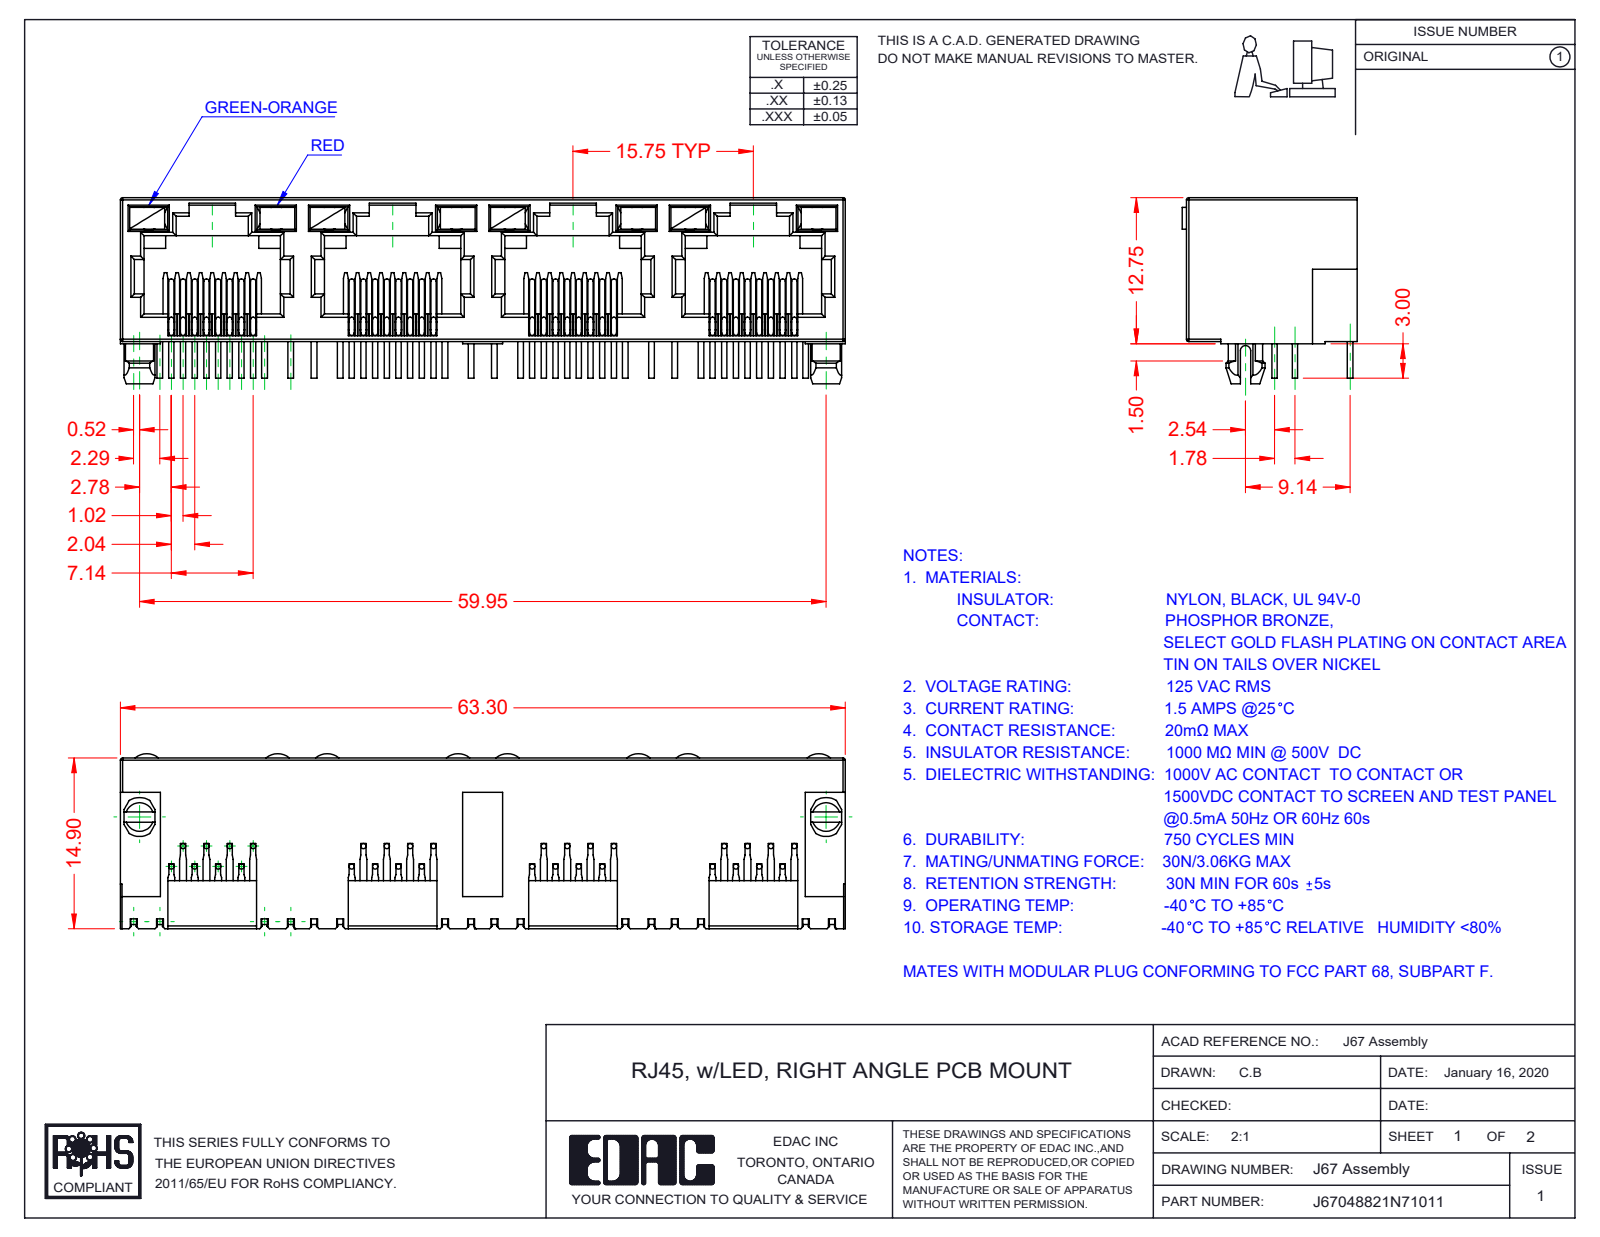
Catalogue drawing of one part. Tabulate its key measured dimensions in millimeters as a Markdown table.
| quantity | value |
| --- | --- |
| part name | J67048822N72011; 67 LED LH_7-Green-Orange; 67 LED RH_2-Red; 67 Contacts (+1 more) |
| STEP written by | SolidWorks 2016 (CONFIG_CONTROL_DESIGN) |
| units | millimeters |
| bodies | 41 solids, 2473 faces (1781 planar, 484 cylindrical, 208 other) |
| overall size | 63.3 × 16.25 × 15.28 |
| volume | 5 159 mm³ |
| surface area | 11 573 mm² |
| round bosses / shafts (diameter × count) | 0.46 × 96 |
| partial cylindrical surfaces (radius × count) | 0.2 × 66, 0.3 × 29, 0.45 × 9, 1.55 × 8, 1.5 × 2, 1.7 × 2, 0.35 × 1, 1 × 1 |
| main face-to-face distances | 0.5, 12.55, 1.89, 0.89, 10, 15.75, 1, 1.39, 11, 11.89 |
